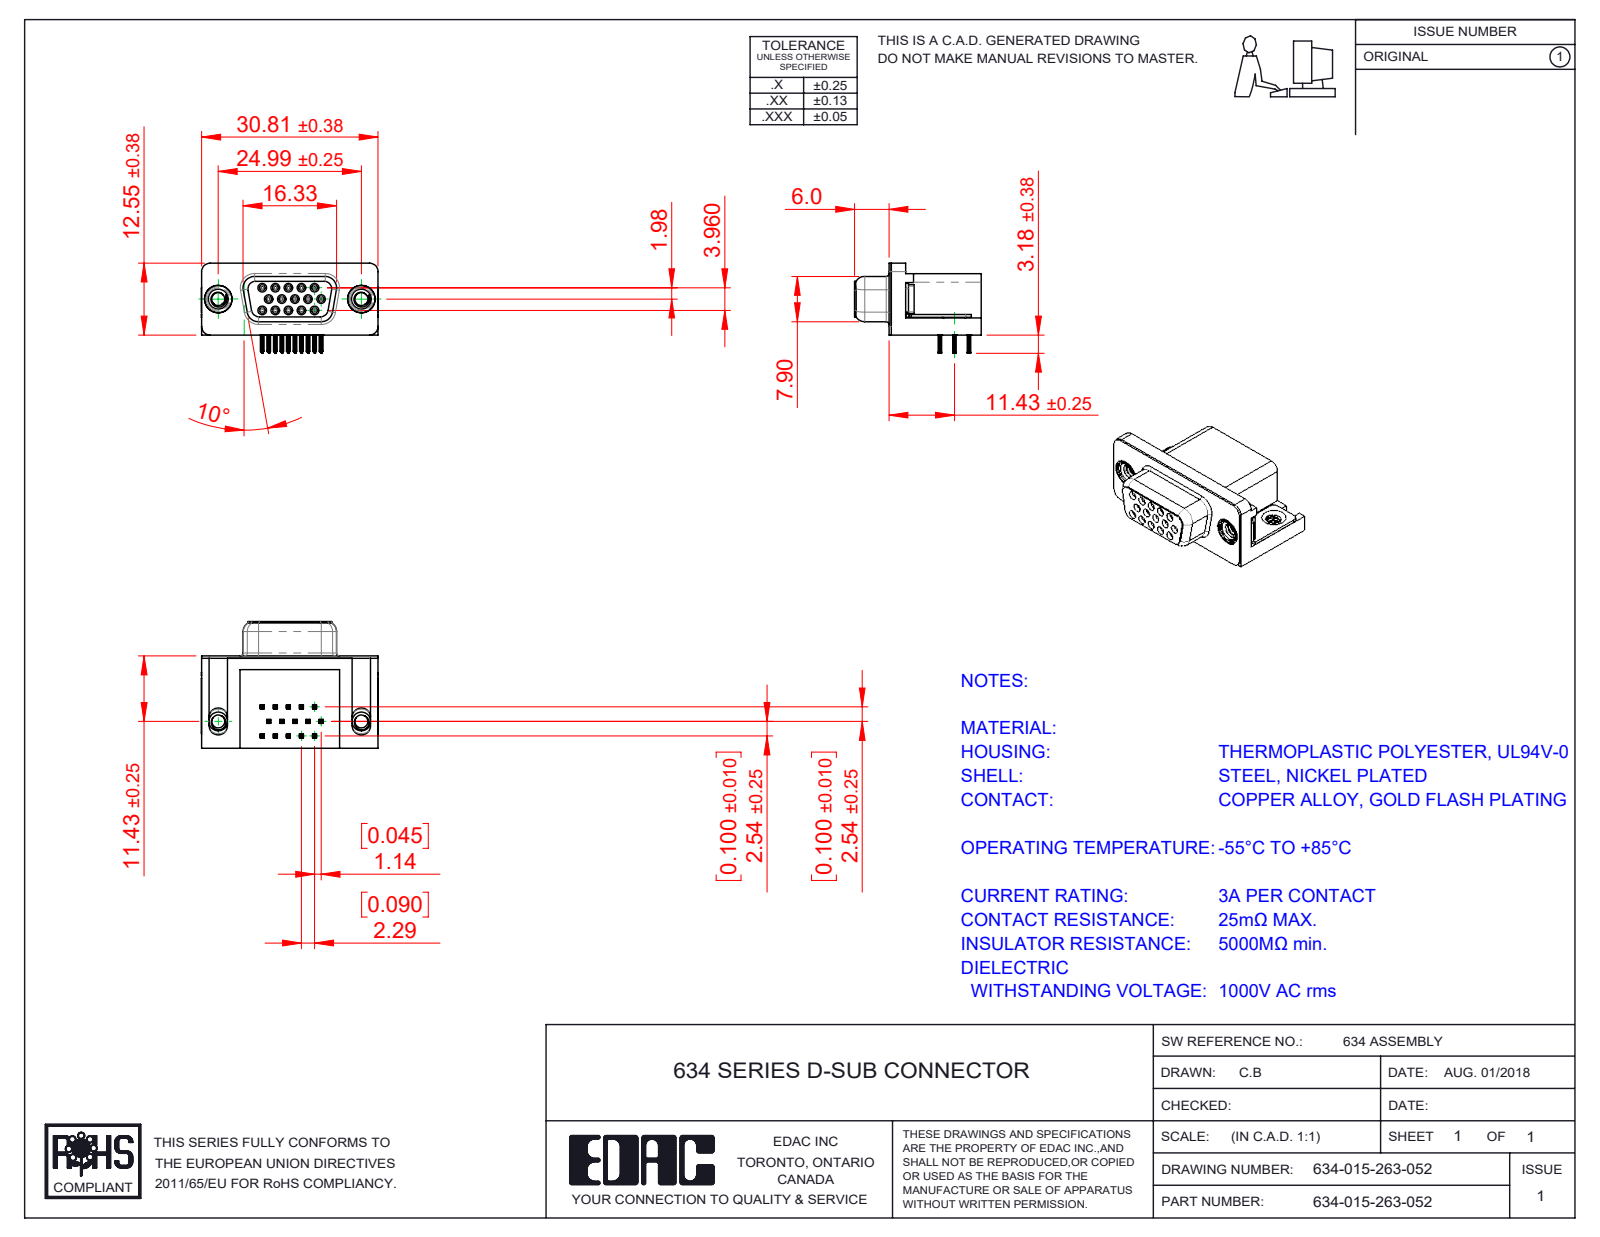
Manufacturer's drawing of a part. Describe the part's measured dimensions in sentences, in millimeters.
The part is named "4-40 Threaded Rivet; Contact Bottom; 634 Shell; Contact Top (+4 more)". Its 3-D file was written by "SolidWorks 2016 (CONFIG_CONTROL_DESIGN)". It is 21 solids with 2451 faces: 1066 planar, 611 cylindrical and 774 other. Overall it measures 30.89 by 22.1 by 15.73 millimeters. Its volume is 4 566 cubic millimeters and its surface area 6 581 square millimeters. Round holes: 15 of diameter 0.8, 15 of diameter 0.9, 4 of diameter 2.26, 2 of diameter 4, 2 of diameter 4.8, 2 of diameter 5. Round bosses or shafts: 15 of diameter 1.2, 2 of diameter 4.9, 2 of diameter 4.75, 2 of diameter 3.9, 2 of diameter 3.26. Partial cylindrical surfaces (rounded edges, fillets, slot ends): 120 of radius 0.1, 60 of radius 0.15, 30 of radius 0.35, 19 of radius 1, 15 of radius 0.34, 8 of radius 0.25, 8 of radius 1.35, 8 of radius 1.6. The main face-to-face distances are 0.4, 10.35, 15.7, 16.1, 0.35, 2.5, 0.6, 2.9, 6.4, 0.5. The hole center spacings are 2.29, 2.28, 3.96, 4.57, 6.05, 3.97, 4.58, 6.86.
